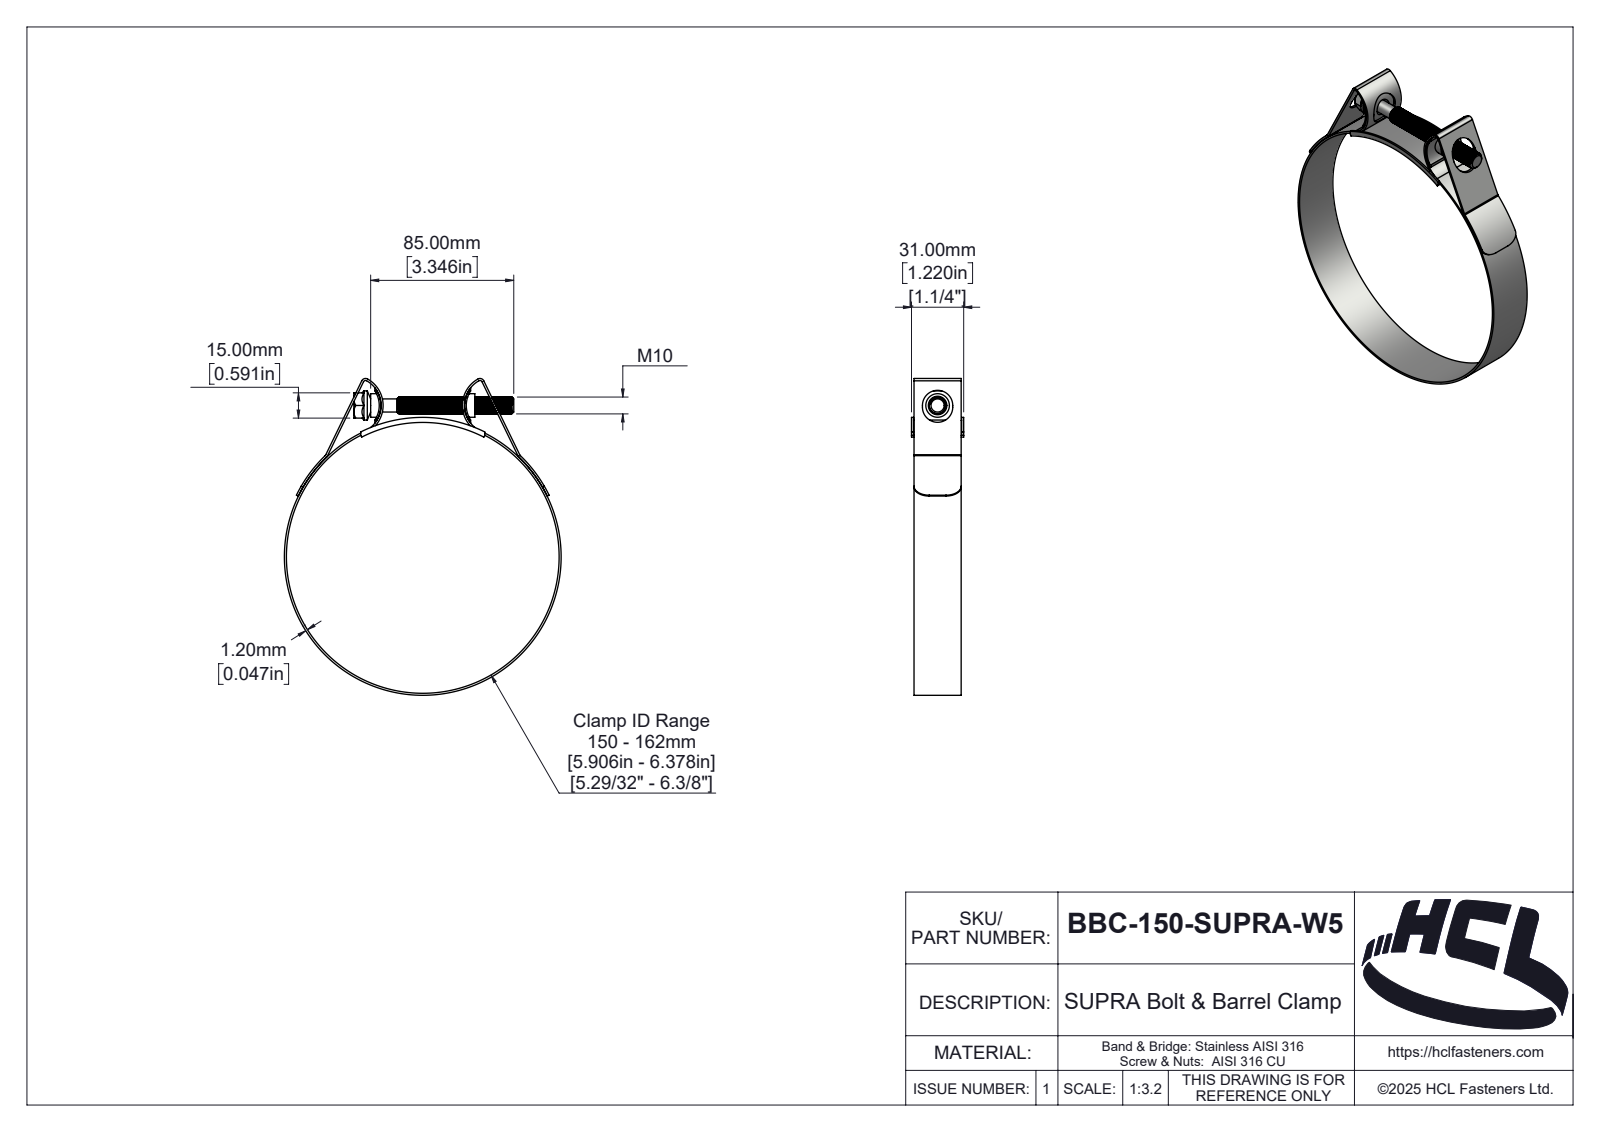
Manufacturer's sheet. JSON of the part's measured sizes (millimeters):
{"part_name": "BBC-150-SUPRA-W5", "step_written_by": "SolidWorks 2025 (AUTOMOTIVE_DESIGN)", "units": "millimeters", "bodies": {"solids": 5, "faces": 381, "planar": 46, "cylindrical": 248, "other": 87}, "overall_size": [188.1, 164.4, 31], "volume_mm3": 33786, "surface_area_mm2": 50786, "round_holes": [[162, 1]], "round_bosses_or_shafts": [[164.4, 1], [17.32, 1], [14, 1], [10, 1], [7.8, 1]], "partial_cylinders_radius": [[1, 4], [1.3, 2], [2, 2], [2.5, 2], [3.2, 2], [9, 2], [15.71, 2], [16.71, 2]], "face_to_face_distances": [1.2, 28, 1.5, 29.5, 29.8, 28.3, 31, 28.6, 15, 2.5]}
